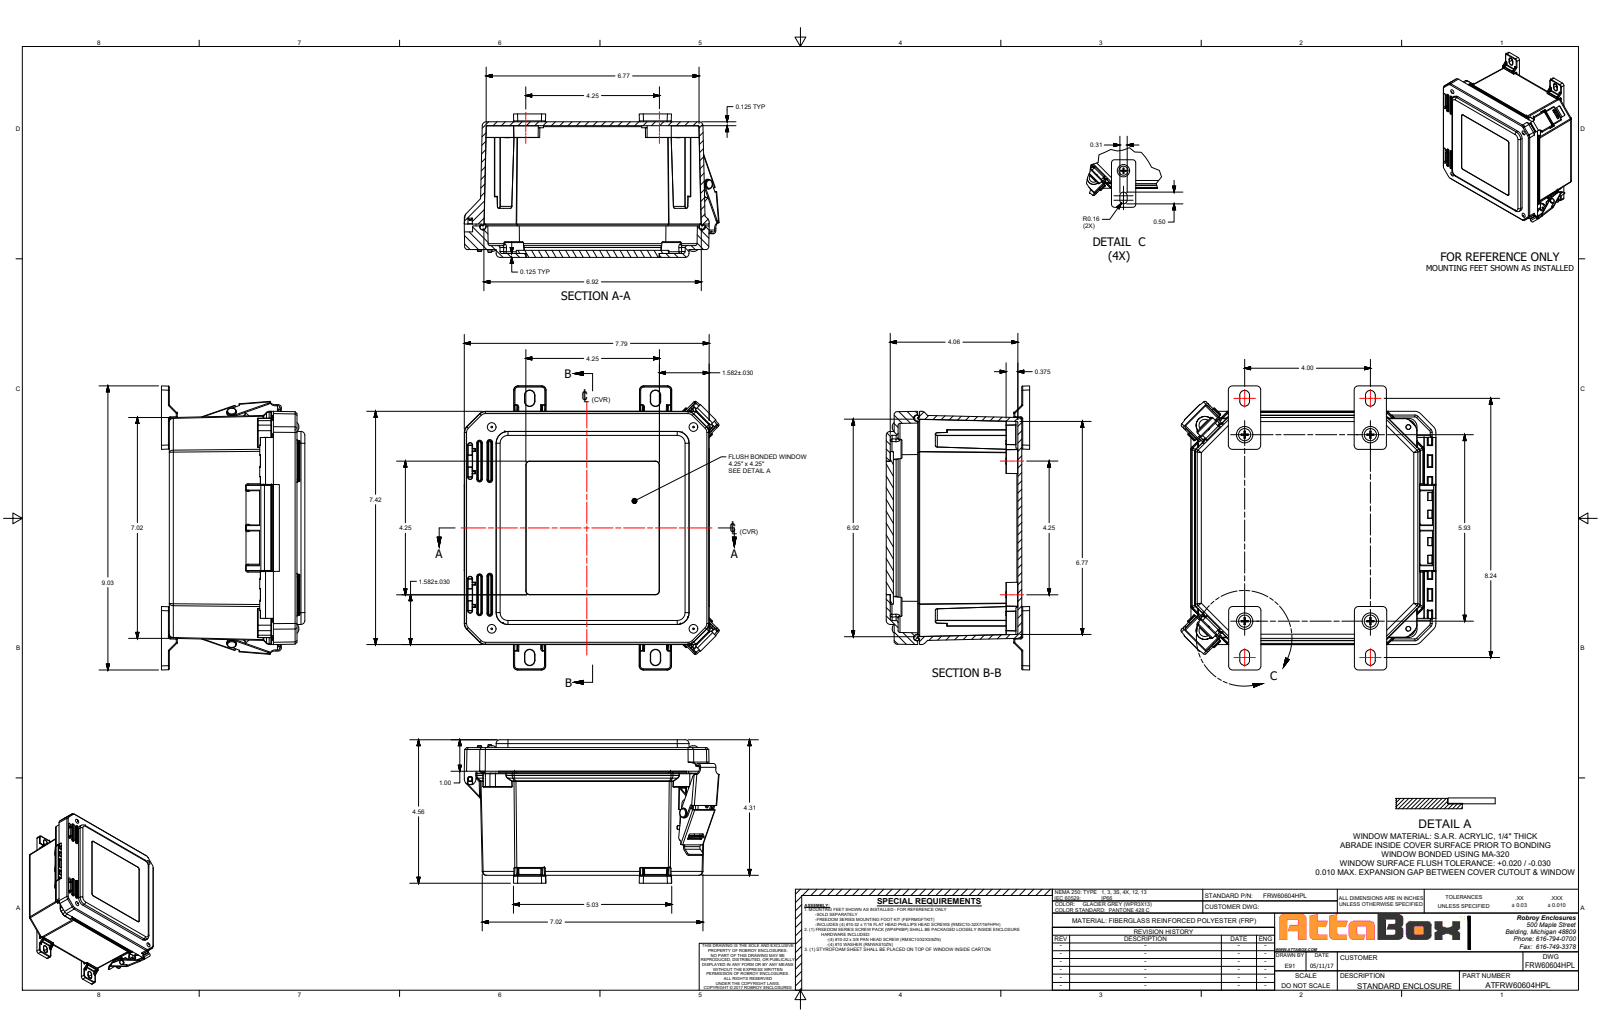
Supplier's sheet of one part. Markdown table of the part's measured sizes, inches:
| quantity | value |
| --- | --- |
| part name | FRW60604HPL |
| STEP written by | SolidWorks 2021 (AUTOMOTIVE_DESIGN) |
| units | inches |
| bodies | 30 solids, 2338 faces (745 planar, 1001 cylindrical, 592 other) |
| overall size | 8.105 × 8.043 × 4.529 |
| volume | 40.58 in³ |
| surface area | 542.9 in² |
| round holes (diameter × count) | 0.135 × 8, 0.152 × 8, 0.159 × 8, 0.135 × 5, 0.15 × 4, 0.156 × 4, 0.252 × 4, 0.253 × 4, 0.137 × 2, 0.219 × 2, 0.227 × 2, 0.313 × 2 |
| round bosses / shafts (diameter × count) | 0.27 × 8, 0.87 × 4, 0.3 × 4, 0.262 × 4, 0.209 × 4, 0.135 × 2, 0.135 × 2, 0.435 × 1 |
| partial cylindrical surfaces (radius × count) | 0.01 × 119, 0.005 × 94, 0.02 × 75, 0.03 × 71, 0.06 × 36, 0.125 × 27, 0.09 × 26, 0.03 × 24 |
| main face-to-face distances | 0.125, 4.184, 0.125, 4.309, 0.25, 3.959, 0.225, 4.084, 3.934, 0.1 |
| hole center spacings | 5.441, 4.25, 5.441, 6.415, 6.414, 0.849, 6.289, 6.552 |
